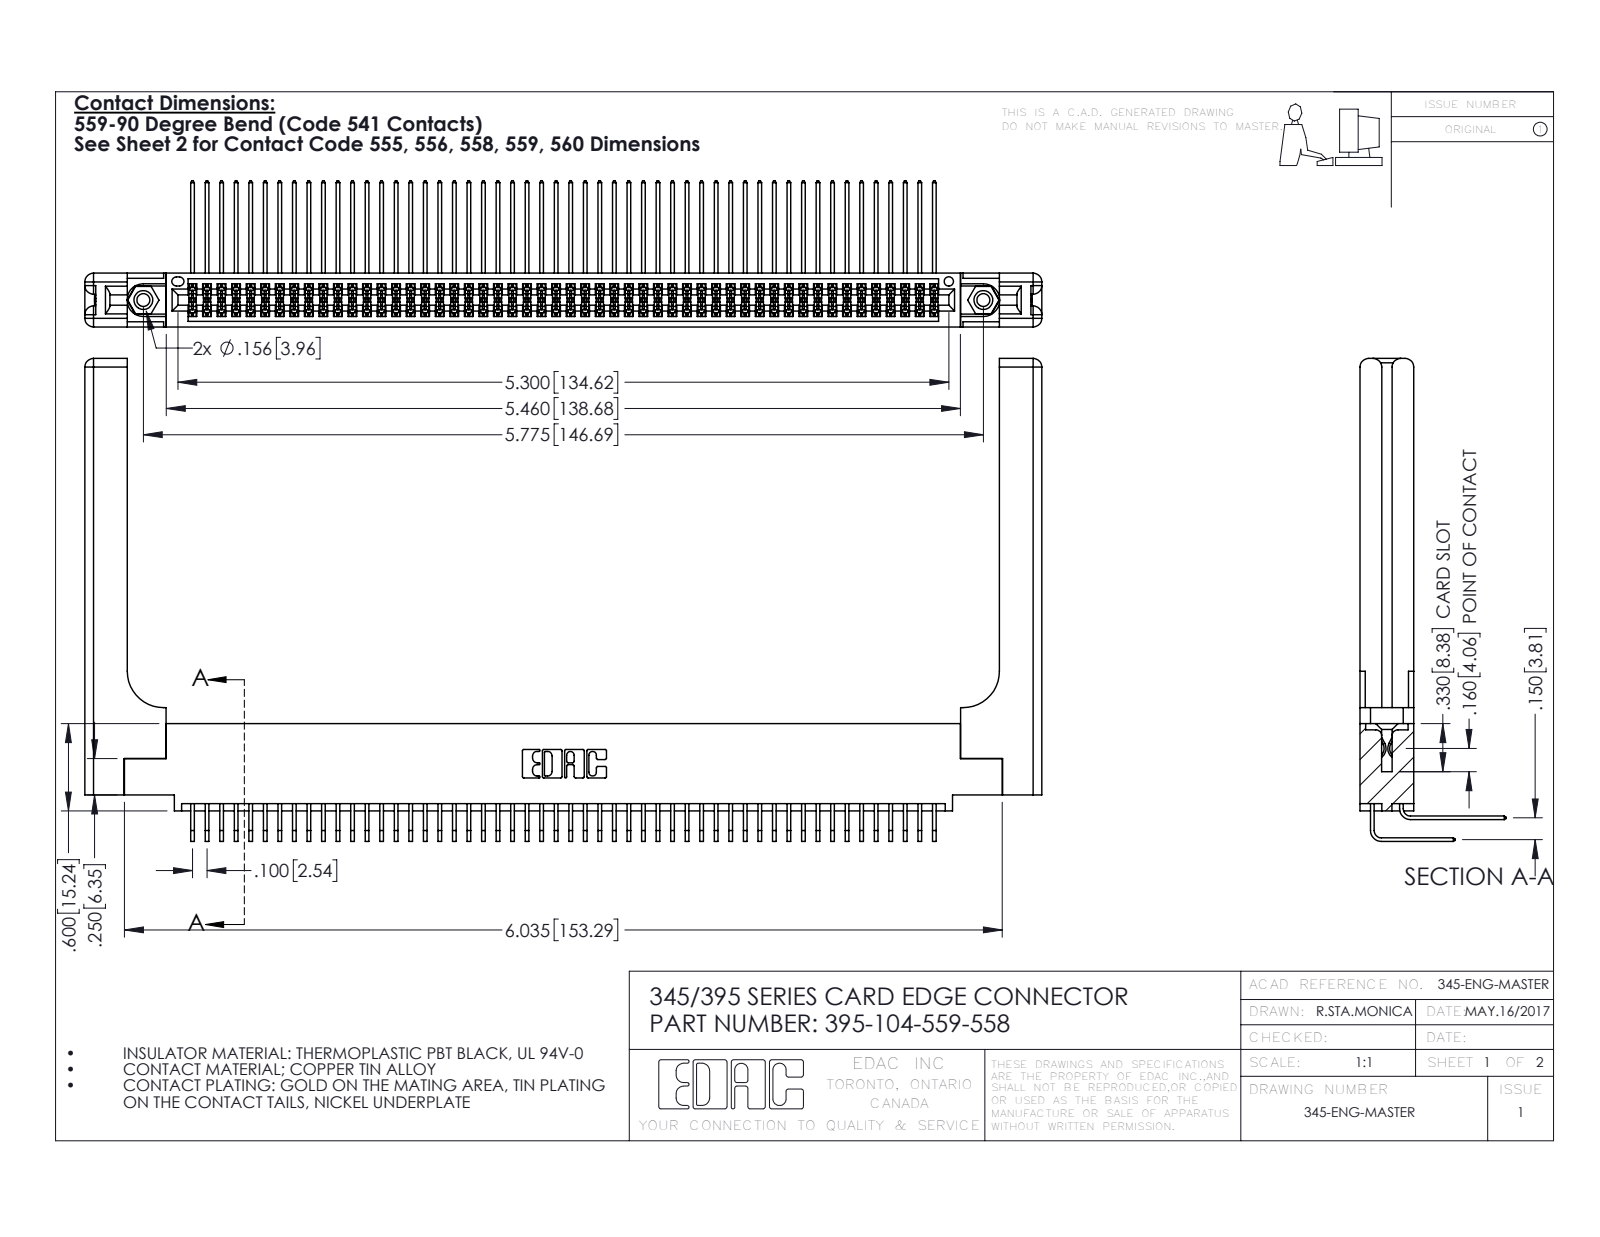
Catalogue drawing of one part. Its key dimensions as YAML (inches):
part_name: "345-292-001_559 Tail - 2; 345-220-058_345-220-058; 395-104-559-558; 345 Part_0.110 Offset - 0.156 Dia-TH (+2 more)"
step_written_by: "SolidWorks 2016 (CONFIG_CONTROL_DESIGN)"
units: inches
bodies: {solids: 109, faces: 5794, planar: 3872, cylindrical: 1862, other: 60}
overall_size: [6.579, 3.319, 1.005]
volume: 1.546
surface_area: 51.27
round_holes:
  - {diameter: 0.089, count: 2}
  - {diameter: 0.125, count: 2}
  - {diameter: 0.156, count: 2}
  - {diameter: 0.064, count: 1}
round_bosses_or_shafts:
  - {diameter: 0.155, count: 2}
partial_cylinders:
  - {radius: 0.006, count: 156}
  - {radius: 0.01, count: 22}
  - {radius: 0.06, count: 16}
  - {radius: 0.007, count: 6}
  - {radius: 0.031, count: 6}
  - {radius: 0.026, count: 3}
  - {radius: 0.014, count: 2}
  - {radius: 0.019, count: 2}
face_to_face_distances: [0.072, 0.298, 0.37, 0.098, 0.272, 0.025, 0.2, 0.225, 0.175, 0.15]
hole_center_spacings: [0.27, 5.539, 5.775]
